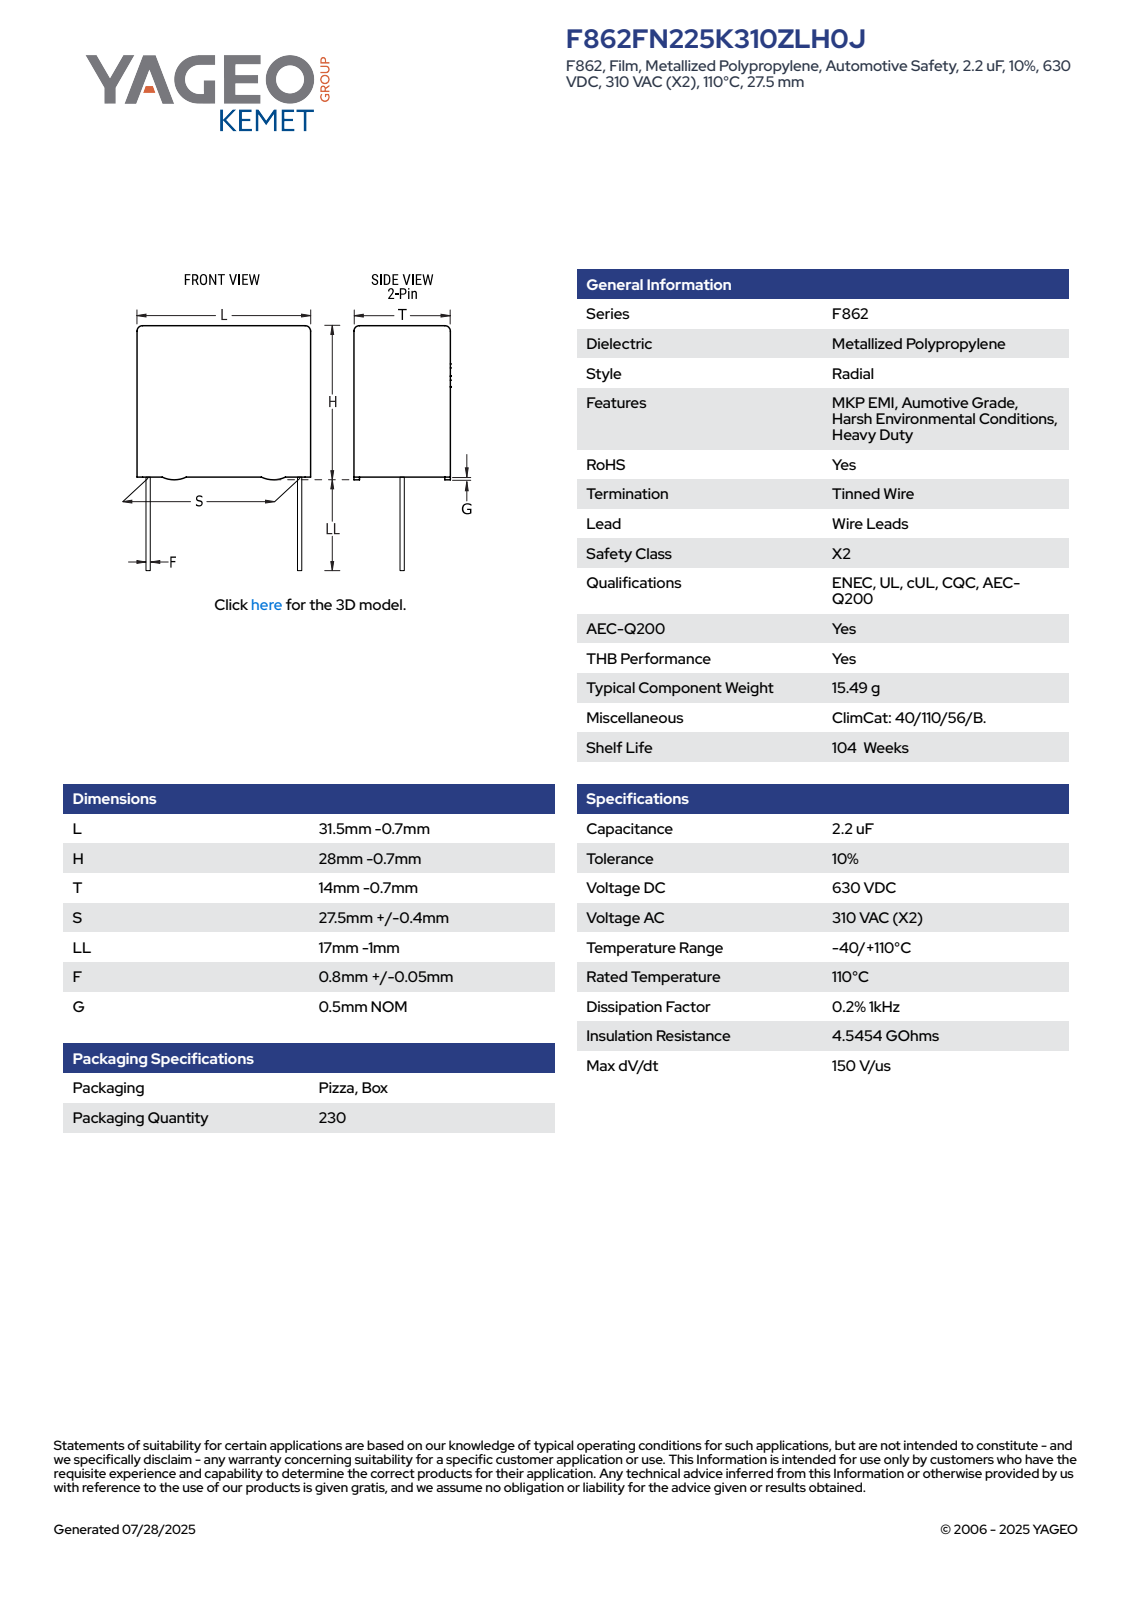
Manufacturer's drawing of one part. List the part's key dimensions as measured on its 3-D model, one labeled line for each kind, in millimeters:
Part name (STEP PRODUCT): CFR_RBG_31.5X28X14_L30.8H27.3T13.3S27.5LL16F0.85G0.5
STEP written by: SolidWorks 2014 (AUTOMOTIVE_DESIGN)
Units: millimetres
Bodies: 4 solids, 89 faces (81 planar, 8 cylindrical, 0 other)
Overall size (bounding box): 43.3 × 30.8 × 13.3
Volume: 11 000 mm³ · Surface area: 3 376 mm²
Round bosses / shafts (diameter × count): ⌀0.85 ×2
Partial cylindrical surfaces — rounded edges, fillets, slot ends (radius × count): R0.5 ×4
Main face-to-face distances: 13.3, 26.8, 30.8, 13.31, 0.5, 27.3, 0.76, 12.54, 0.77, 11.78
